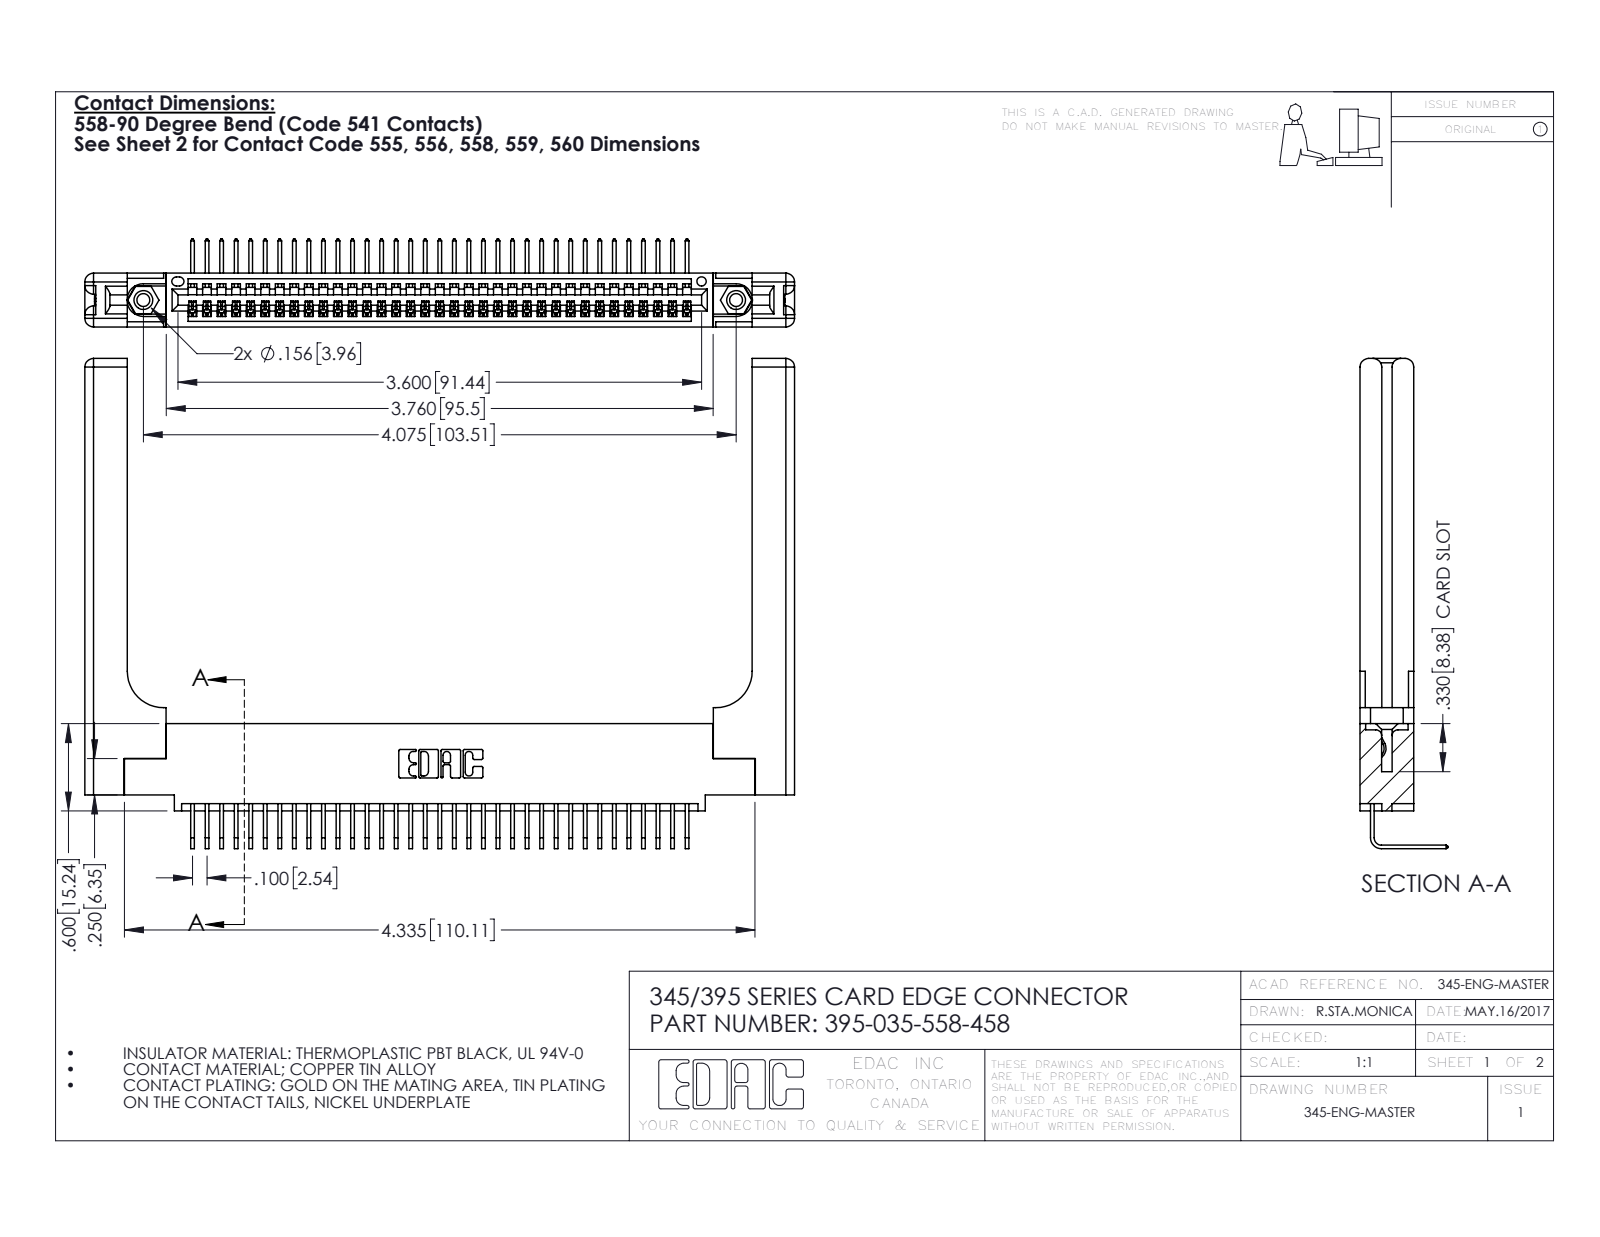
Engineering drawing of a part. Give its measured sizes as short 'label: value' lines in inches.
name: 345-250-001_345-250-001-102; 345 Part_0.110 Offset - 0.156 Dia-TH; 395-035-558-458; 345-292-001_558 Tail - 2 (+1 more)
written by: SolidWorks 2016 (CONFIG_CONTROL_DESIGN)
unit: in
bodies: 40 solids, 2486 faces (1702 planar, 724 cylindrical, 60 other)
size: 4.879 × 3.369 × 0.605
volume: 1.236 in³; area: 33.48 in²
holes: 2× ⌀0.089, 2× ⌀0.125, 2× ⌀0.156, 1× ⌀0.064
bosses: 2× ⌀0.155
rounds: 70× R0.006, 22× R0.01, 16× R0.06, 6× R0.007, 6× R0.031, 3× R0.026, 2× R0.03, 2× R0.031
face distances: 0.37, 0.072, 0.298, 0.098, 0.272, 0.025, 0.2, 0.148, 0.15, 0.225
hole spacings: 0.27, 3.839, 4.075
